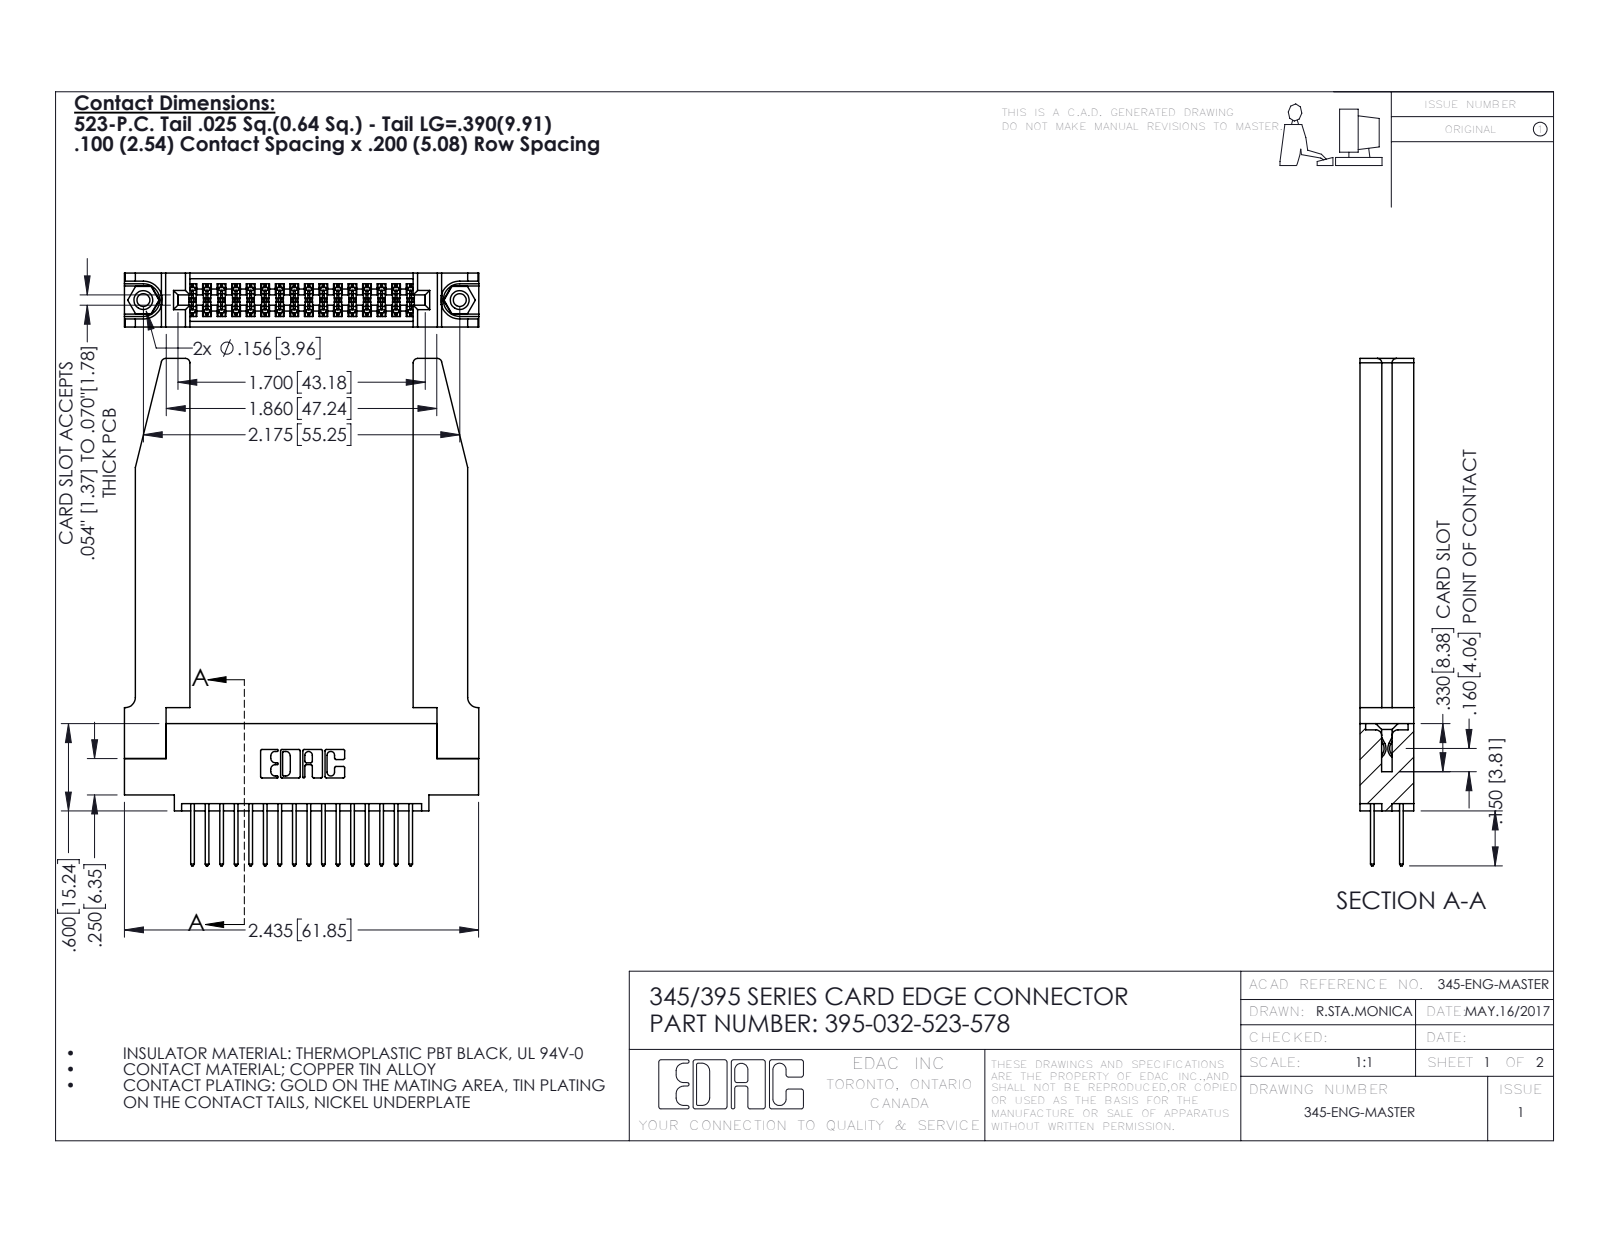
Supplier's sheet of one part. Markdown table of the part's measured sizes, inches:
| quantity | value |
| --- | --- |
| part name | 345-220-078_345-220-078; 345-292-001_345-293-123; 395-032-523-578; 345 Part_0.110 Offset - 0.156 Dia-TH (+1 more) |
| STEP written by | SolidWorks 2016 (CONFIG_CONTROL_DESIGN) |
| units | inches |
| bodies | 37 solids, 1964 faces (1282 planar, 630 cylindrical, 52 other) |
| overall size | 3.487 × 2.436 × 0.37 |
| volume | 0.826 in³ |
| surface area | 23.62 in² |
| round holes (diameter × count) | 0.089 × 2, 0.125 × 2, 0.156 × 2, 0.064 × 1 |
| round bosses / shafts (diameter × count) | 0.155 × 2 |
| partial cylindrical surfaces (radius × count) | 0.006 × 48, 0.01 × 32, 0.01 × 22, 0.03 × 8, 0.007 × 6, 0.031 × 6, 0.026 × 3, 0.014 × 2 |
| main face-to-face distances | 0.37, 0.072, 0.298, 0.2, 0.098, 0.272, 0.025, 0.148, 0.15, 0.225 |
| hole center spacings | 0.27, 1.942, 2.175 |
